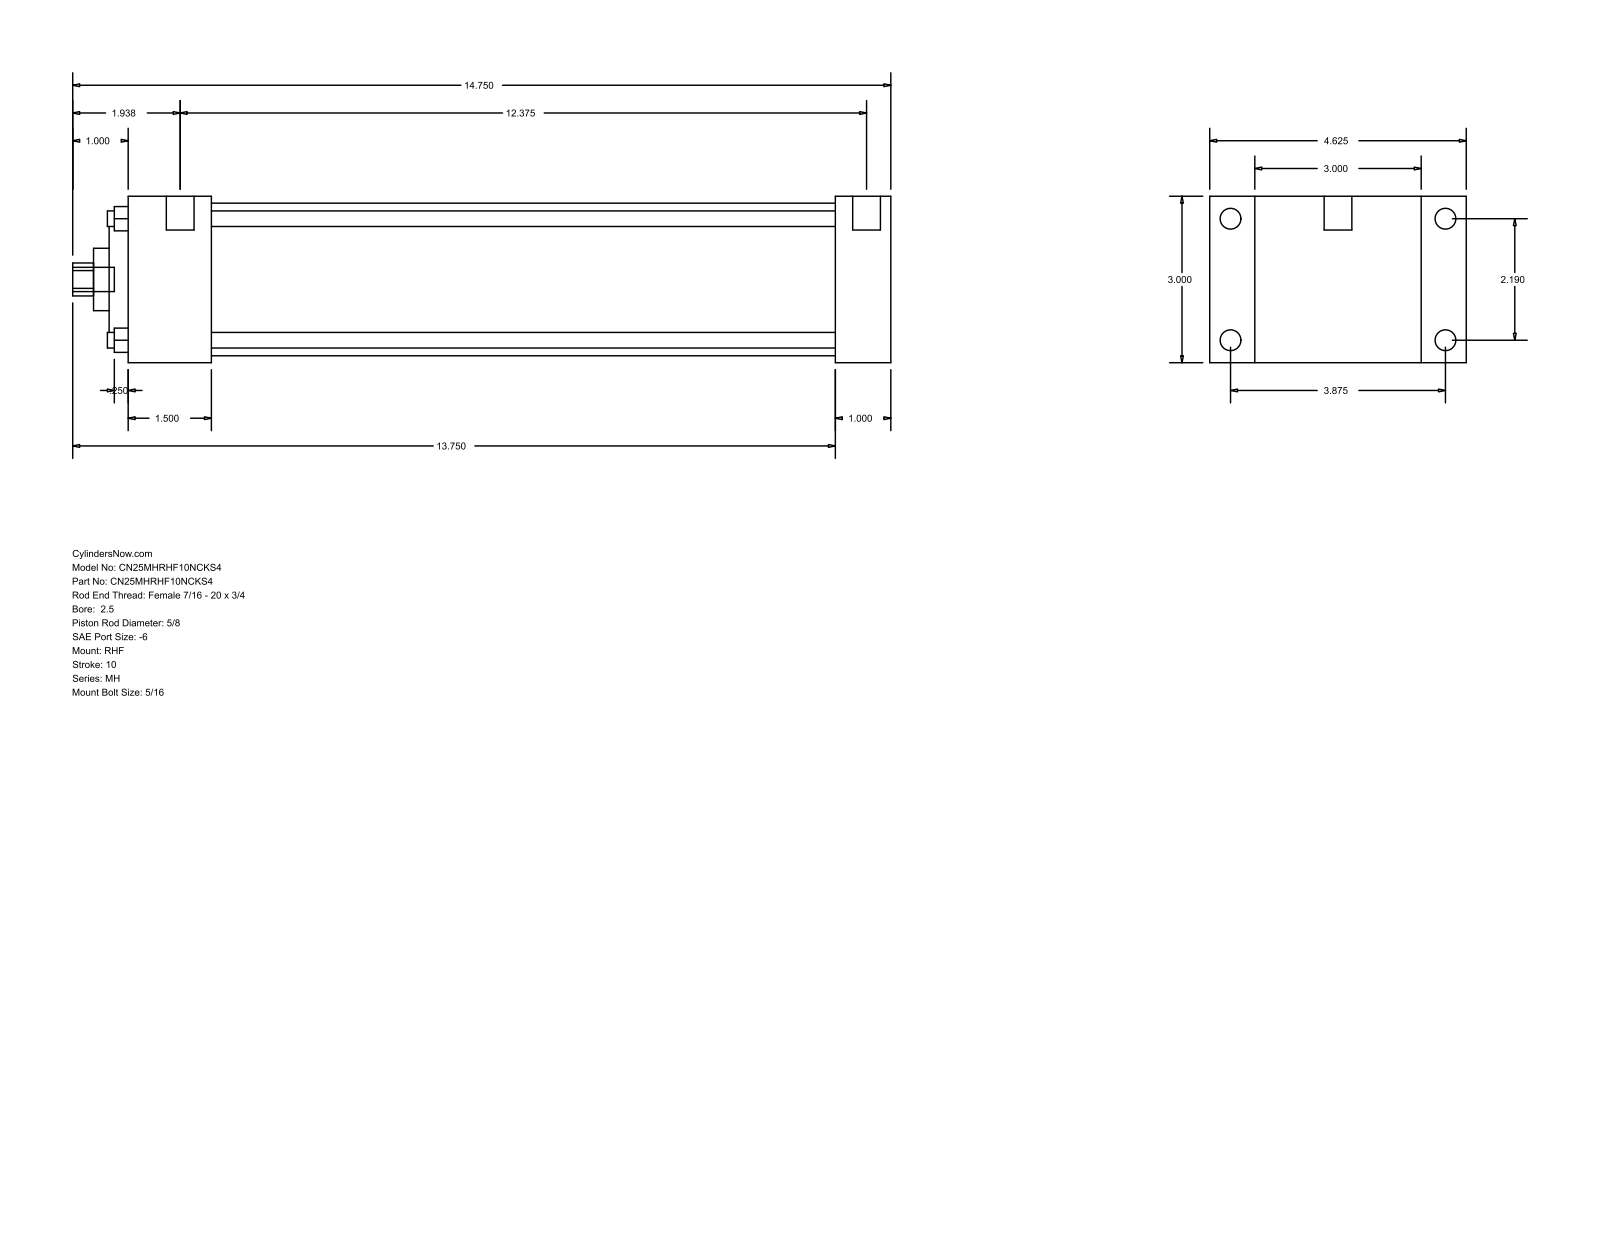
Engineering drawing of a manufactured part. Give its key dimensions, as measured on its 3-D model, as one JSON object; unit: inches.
{"part_name": "MH_RHF__0250_0.625", "step_written_by": "GSSL Pune (CONFIG_CONTROL_DESIGN)", "units": "inches", "bodies": {"solids": 0, "faces": 90, "planar": 61, "cylindrical": 29, "other": 0}, "overall_size": [14.75, 4.625, 3], "round_holes": [[0.281, 4], [0.625, 1], [1.125, 1], [2.187, 1], [2.75, 1]], "round_bosses_or_shafts": [[0.375, 4], [0.219, 4], [0.5, 2], [0.437, 1]], "partial_cylinders_radius": [[0.297, 1]], "face_to_face_distances": [3, 1, 0.813, 3.813, 13.75, 12.75, 4.625, 1.5, 11.25, 12.25], "hole_center_spacings": [1.548, 2.19, 3.097]}
